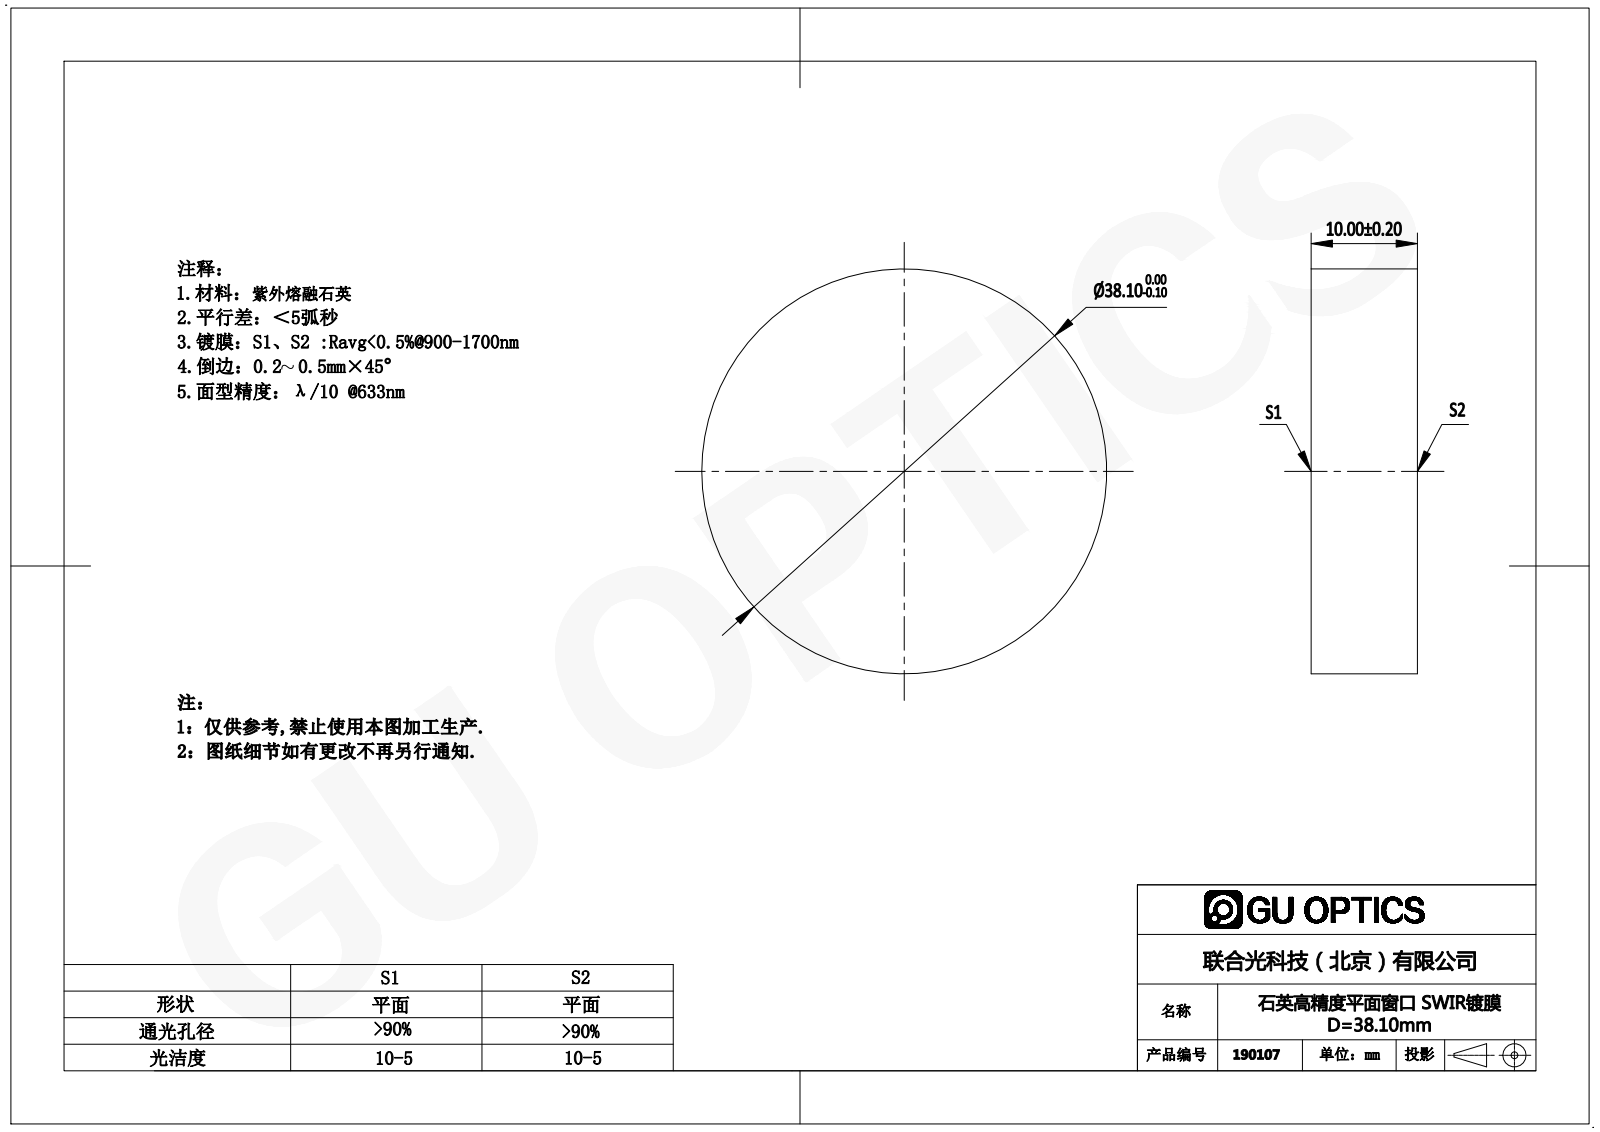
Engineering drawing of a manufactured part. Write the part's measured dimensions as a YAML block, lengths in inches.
part_name: "190063"
step_written_by: "SolidWorks 2016 (AUTOMOTIVE_DESIGN)"
units: inches
bodies: {solids: 1, faces: 4, planar: 2, cylindrical: 2, other: 0}
overall_size: [1.5, 1.5, 0.394]
volume: 0.696
surface_area: 5.389
round_bosses_or_shafts:
  - {diameter: 1.5, count: 1}
face_to_face_distances: [0.394]
